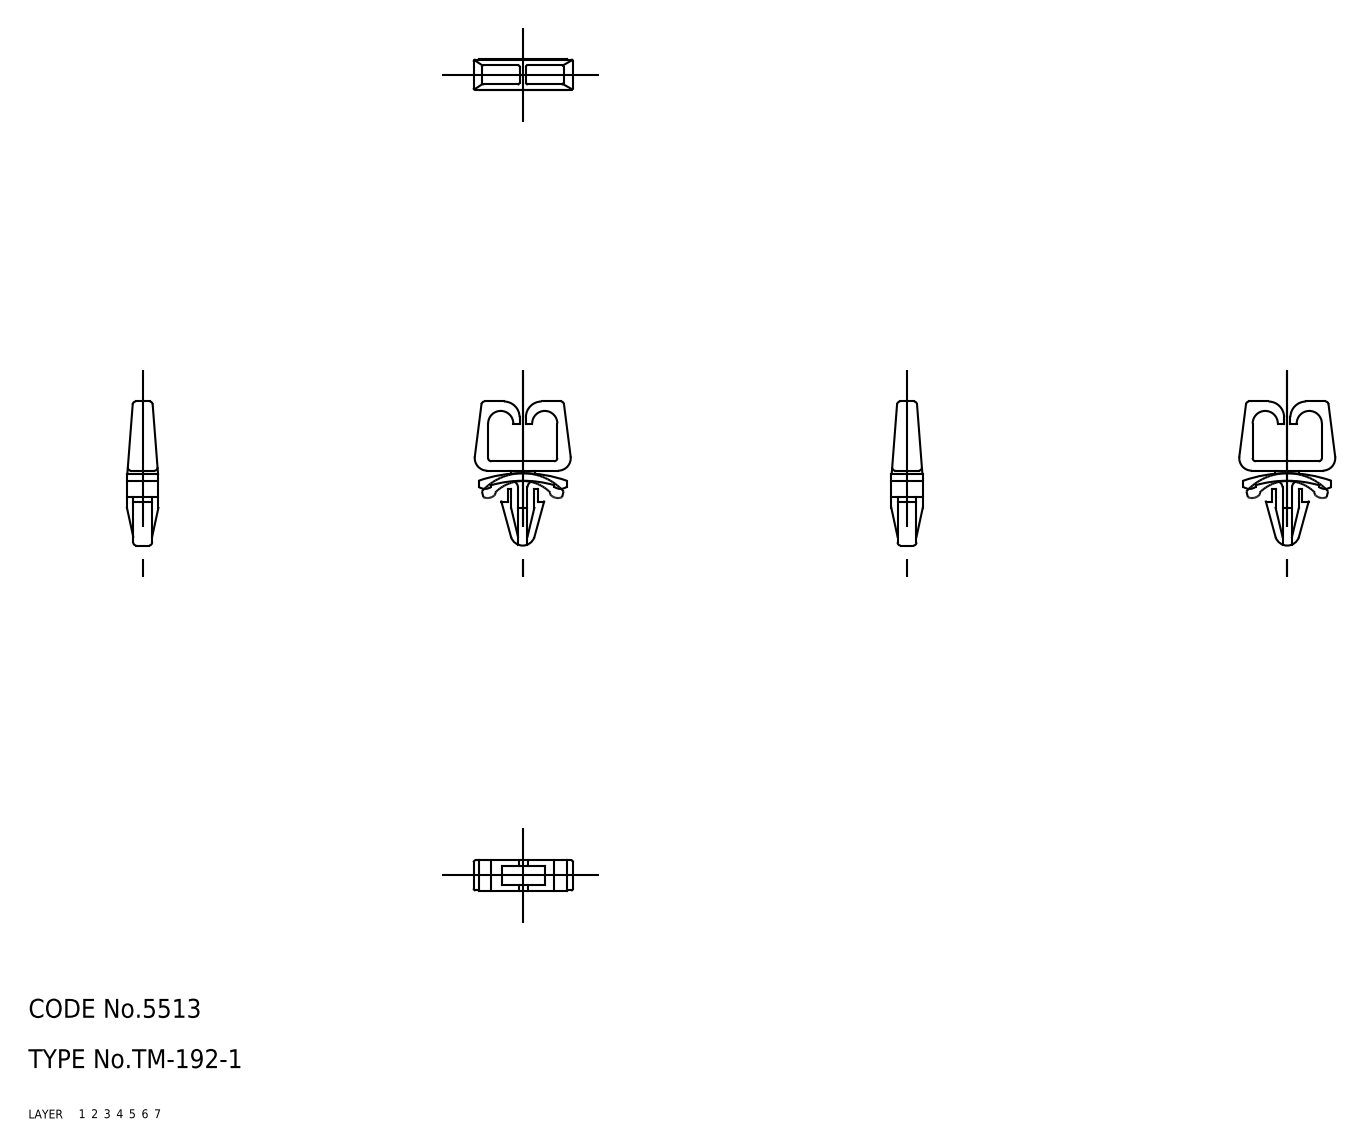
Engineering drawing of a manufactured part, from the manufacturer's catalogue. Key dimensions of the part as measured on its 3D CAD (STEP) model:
Part name (STEP PRODUCT): clip
STEP written by: CADfix (AUTOMOTIVE_DESIGN)
Units: millimetres
Bodies: 1 solid, 108 faces (0 planar, 0 cylindrical, 108 other)
Overall size (bounding box): 22.9 × 15.26 × 5
Volume: 489 mm³ · Surface area: 862 mm²
